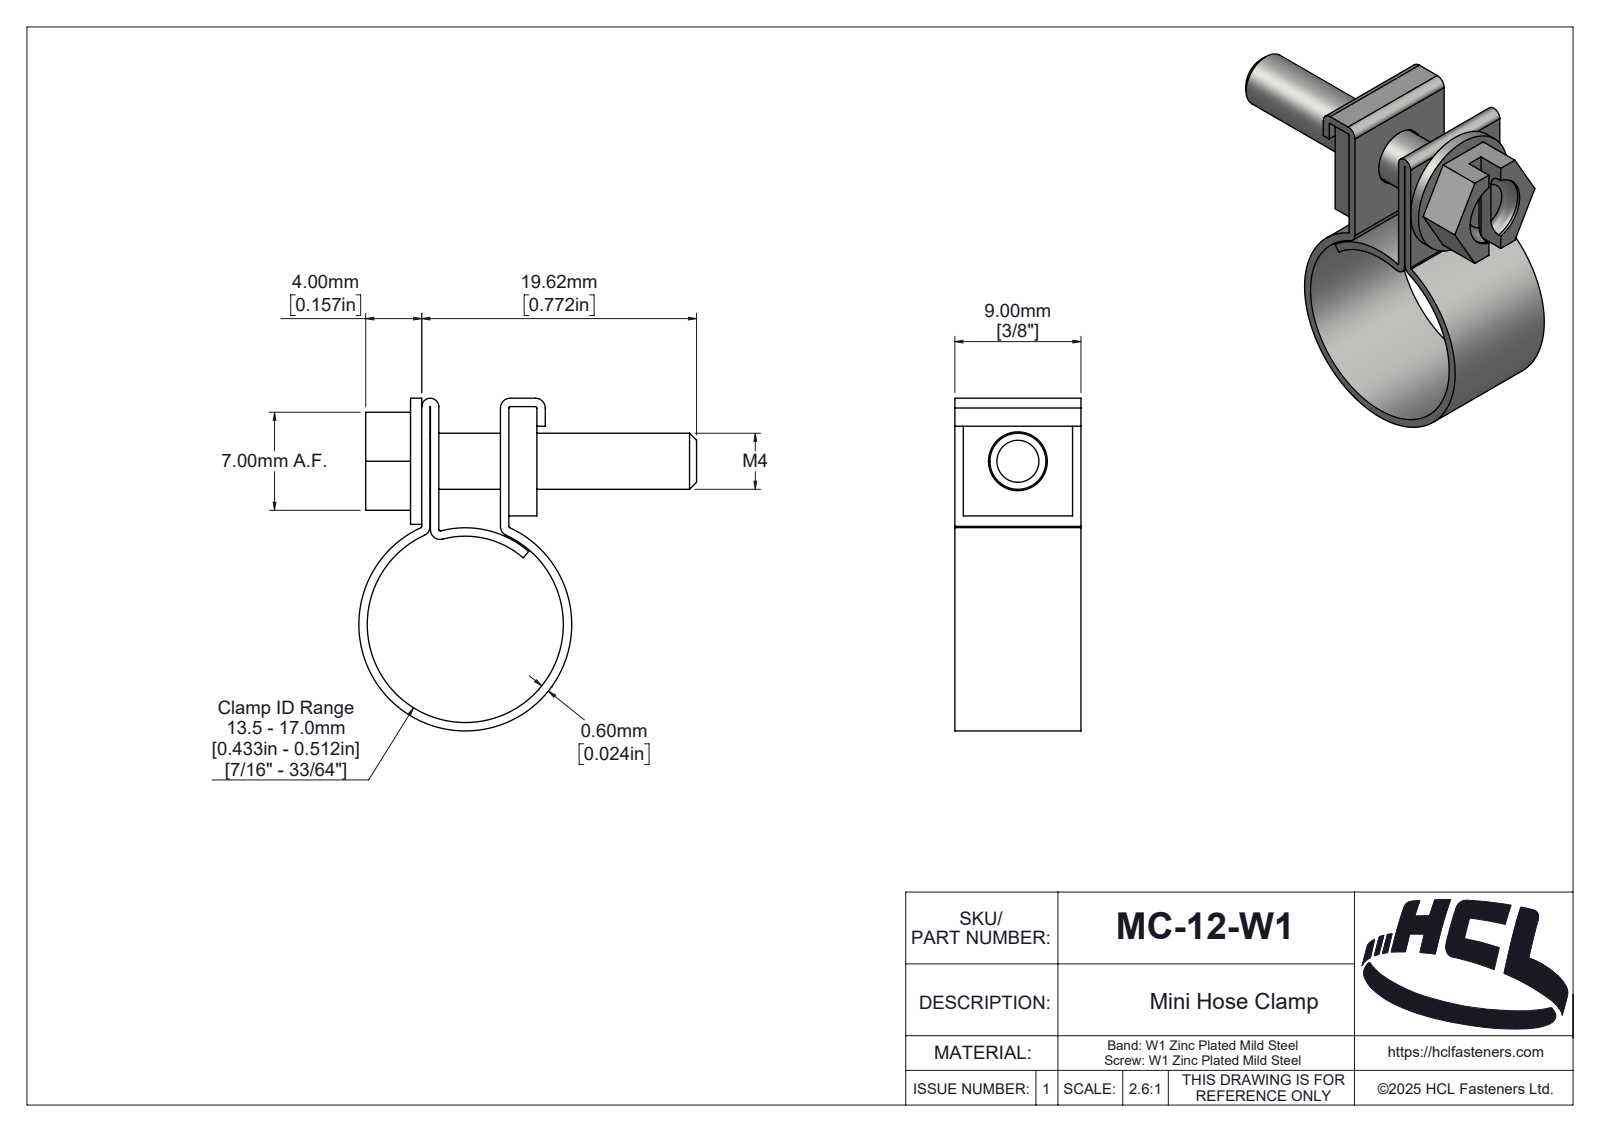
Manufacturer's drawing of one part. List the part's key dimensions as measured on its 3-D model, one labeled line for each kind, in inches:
Part name (STEP PRODUCT): MC-12-W1
STEP written by: SolidWorks 2025 (AUTOMOTIVE_DESIGN)
Units: inches
Bodies: 3 solids, 175 faces (38 planar, 84 cylindrical, 53 other)
Overall size (bounding box): 0.949 × 0.935 × 0.354
Volume: 0.055 in³ · Surface area: 3.32 in²
Round holes (diameter × count): ⌀0.165 ×1, ⌀0.197 ×1, ⌀0.551 ×1
Round bosses / shafts (diameter × count): ⌀0.598 ×1, ⌀0.354 ×1, ⌀0.157 ×1
Partial cylindrical surfaces — rounded edges, fillets, slot ends (radius × count): R0.004 ×5, R0.028 ×5, R0.008 ×1, R0.024 ×1, R0.032 ×1, R0.04 ×1, R0.042 ×1, R0.05 ×1
Main face-to-face distances: 0.024, 0.024, 0.197, 0.221, 0.245, 0.276, 0.079, 0.102, 0.324, 0.299
